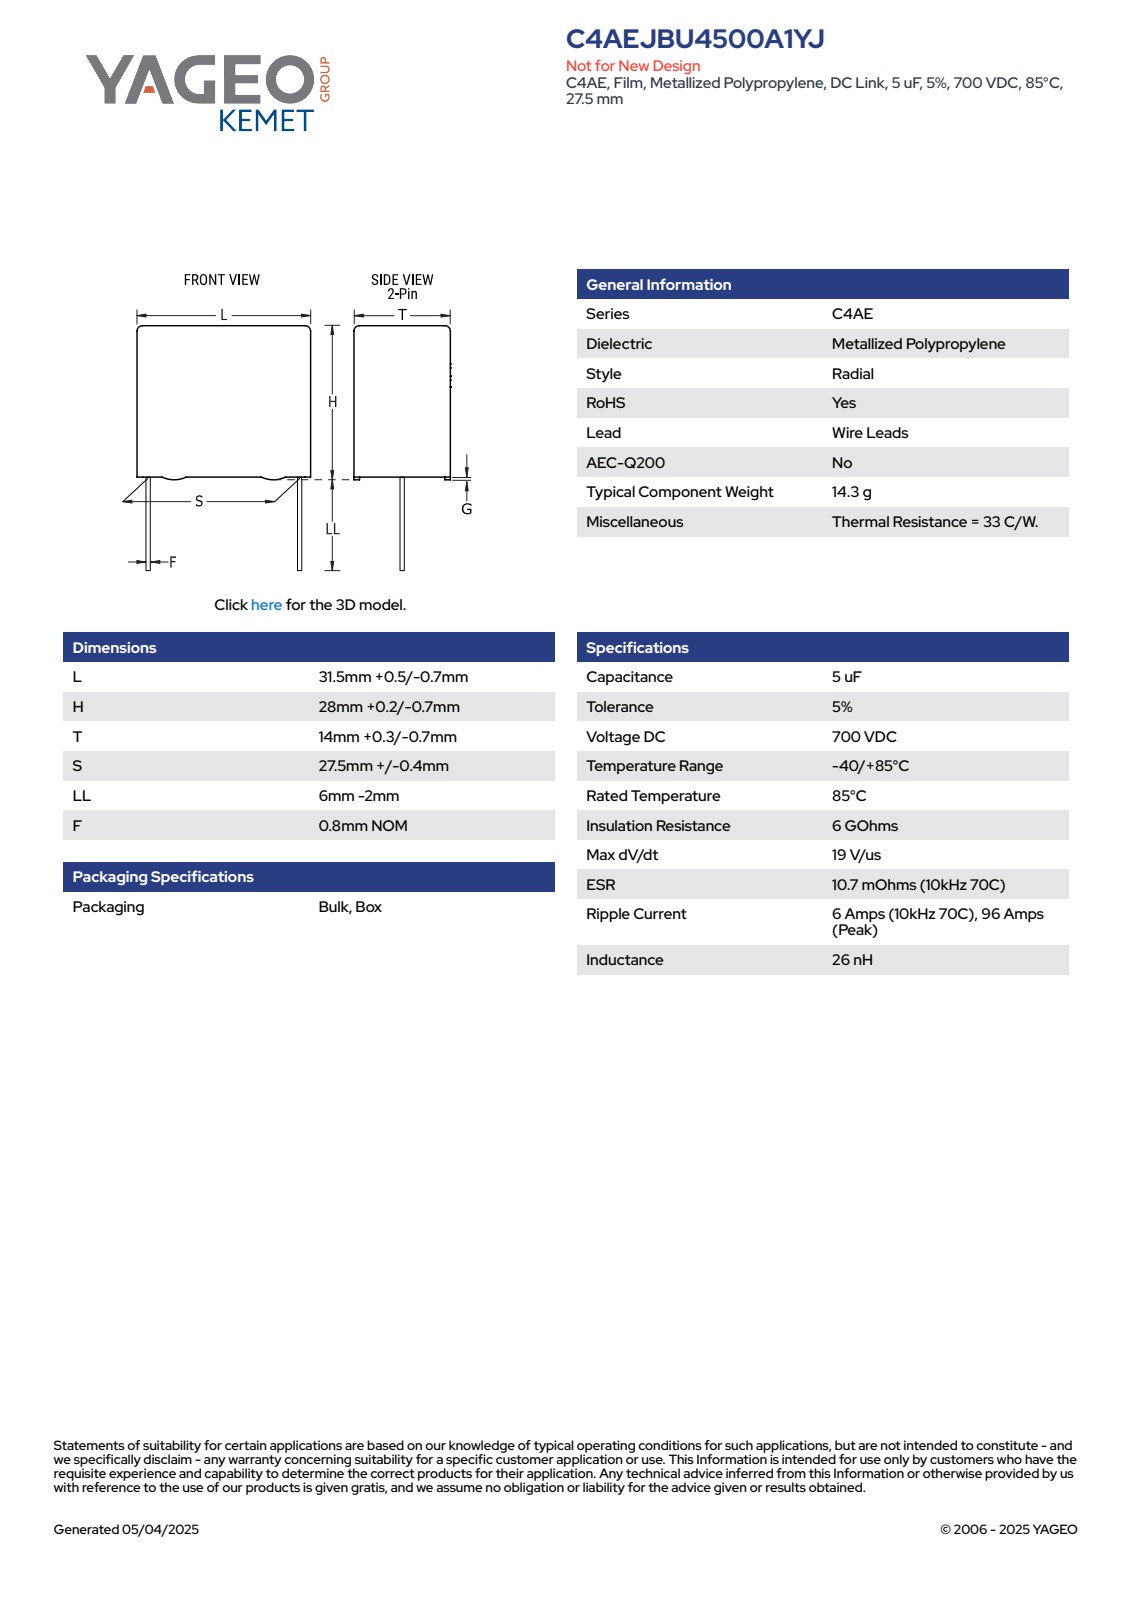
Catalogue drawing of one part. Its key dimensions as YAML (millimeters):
part_name: "CFP_RBG_31.5X28X14_L32H28.2T14.3S27.9LL4F0.8G0.5"
step_written_by: "SolidWorks 2014 (AUTOMOTIVE_DESIGN)"
units: millimeters
bodies: {solids: 4, faces: 89, planar: 81, cylindrical: 8, other: 0}
overall_size: [32.2, 32, 14.3]
volume: 12688
surface_area: 3604
round_bosses_or_shafts:
  - {diameter: 0.8, count: 2}
partial_cylinders:
  - {radius: 0.5, count: 4}
face_to_face_distances: [14.3, 27.7, 32, 0.5, 28.2, 1.27, 13.03, 11.76, 18.78, 4]
